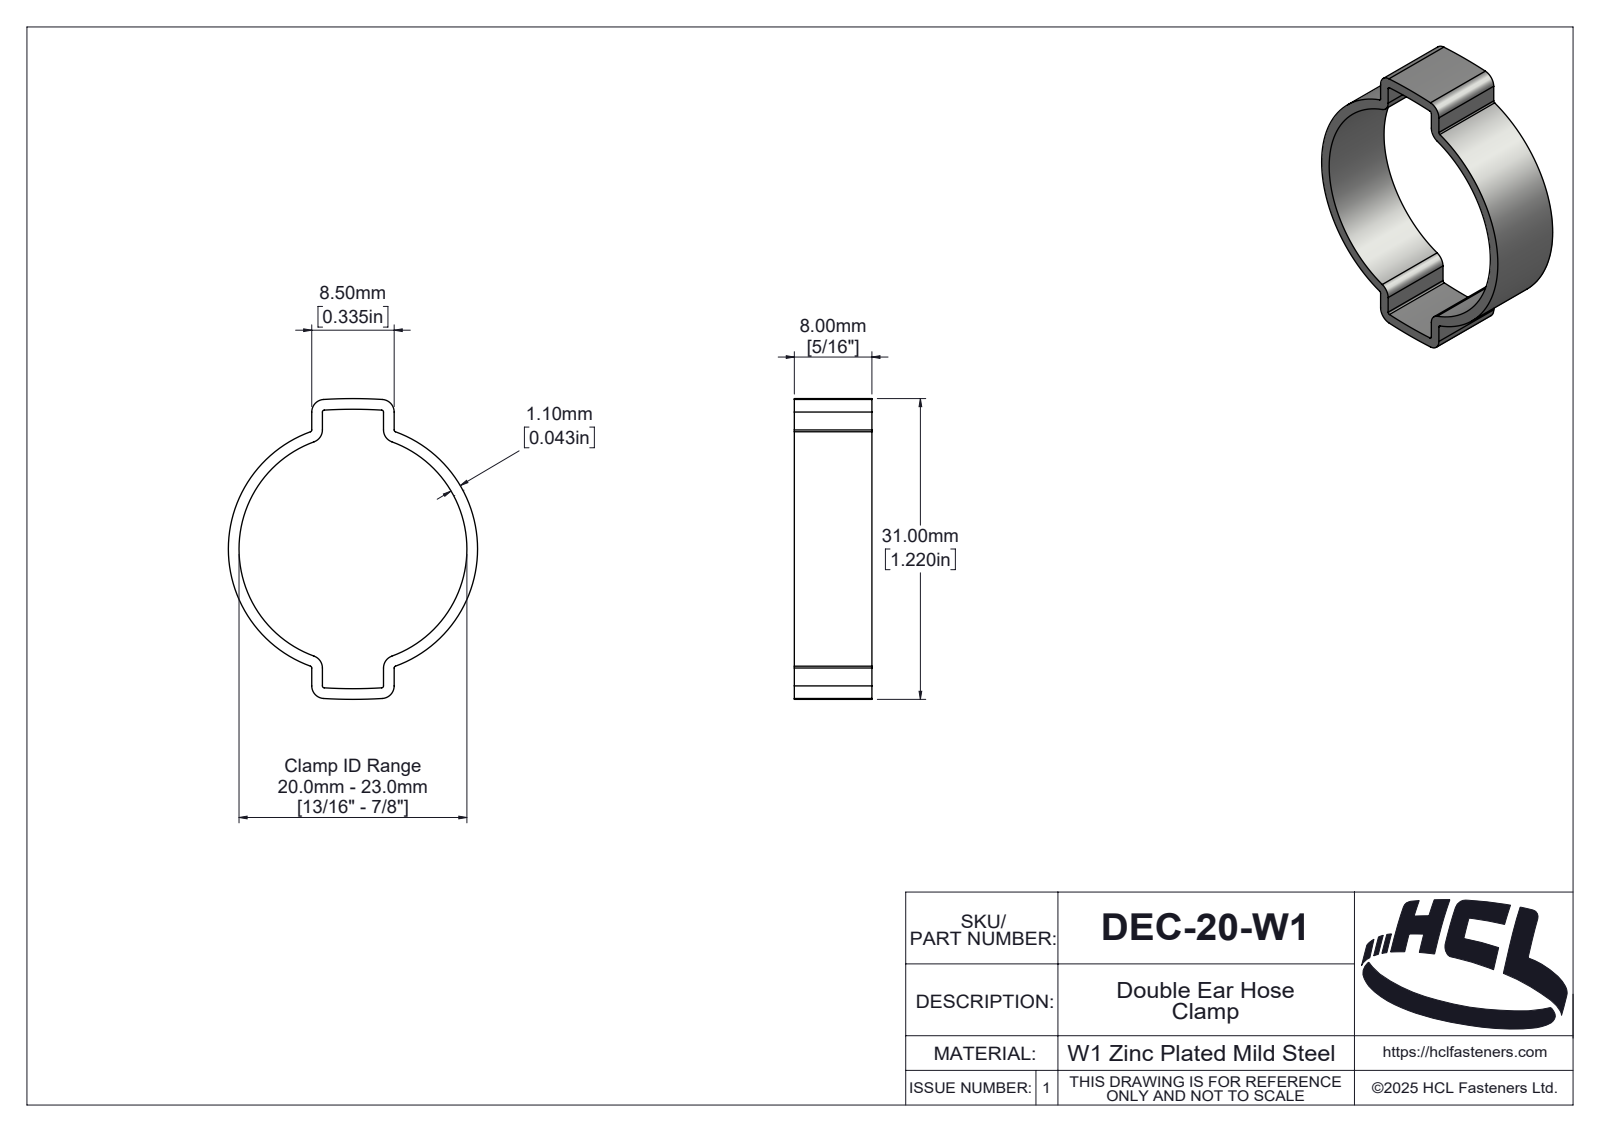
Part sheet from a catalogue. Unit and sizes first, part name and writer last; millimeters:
Units: millimetres
Overall size (bounding box): 31 × 25.7 × 8
Partial cylindrical surfaces — rounded edges, fillets, slot ends (radius × count): R0.2 ×8, R1.3 ×8, R49.66 ×2, R50.76 ×2, R0.2 ×1, R0.81 ×1, R1.01 ×1, R1.06 ×1
Main face-to-face distances: 8, 1.1, 7.4, 8.5, 6.3, 4.13, 3.03, 3.27, 4.37, 3.98
Volume: 772 mm³ · Surface area: 1 600 mm²
Bodies: 1 solid, 139 faces (12 planar, 69 cylindrical, 58 other)
Part name (STEP PRODUCT): DEC-20-W1
STEP written by: SolidWorks 2025 (AUTOMOTIVE_DESIGN)
